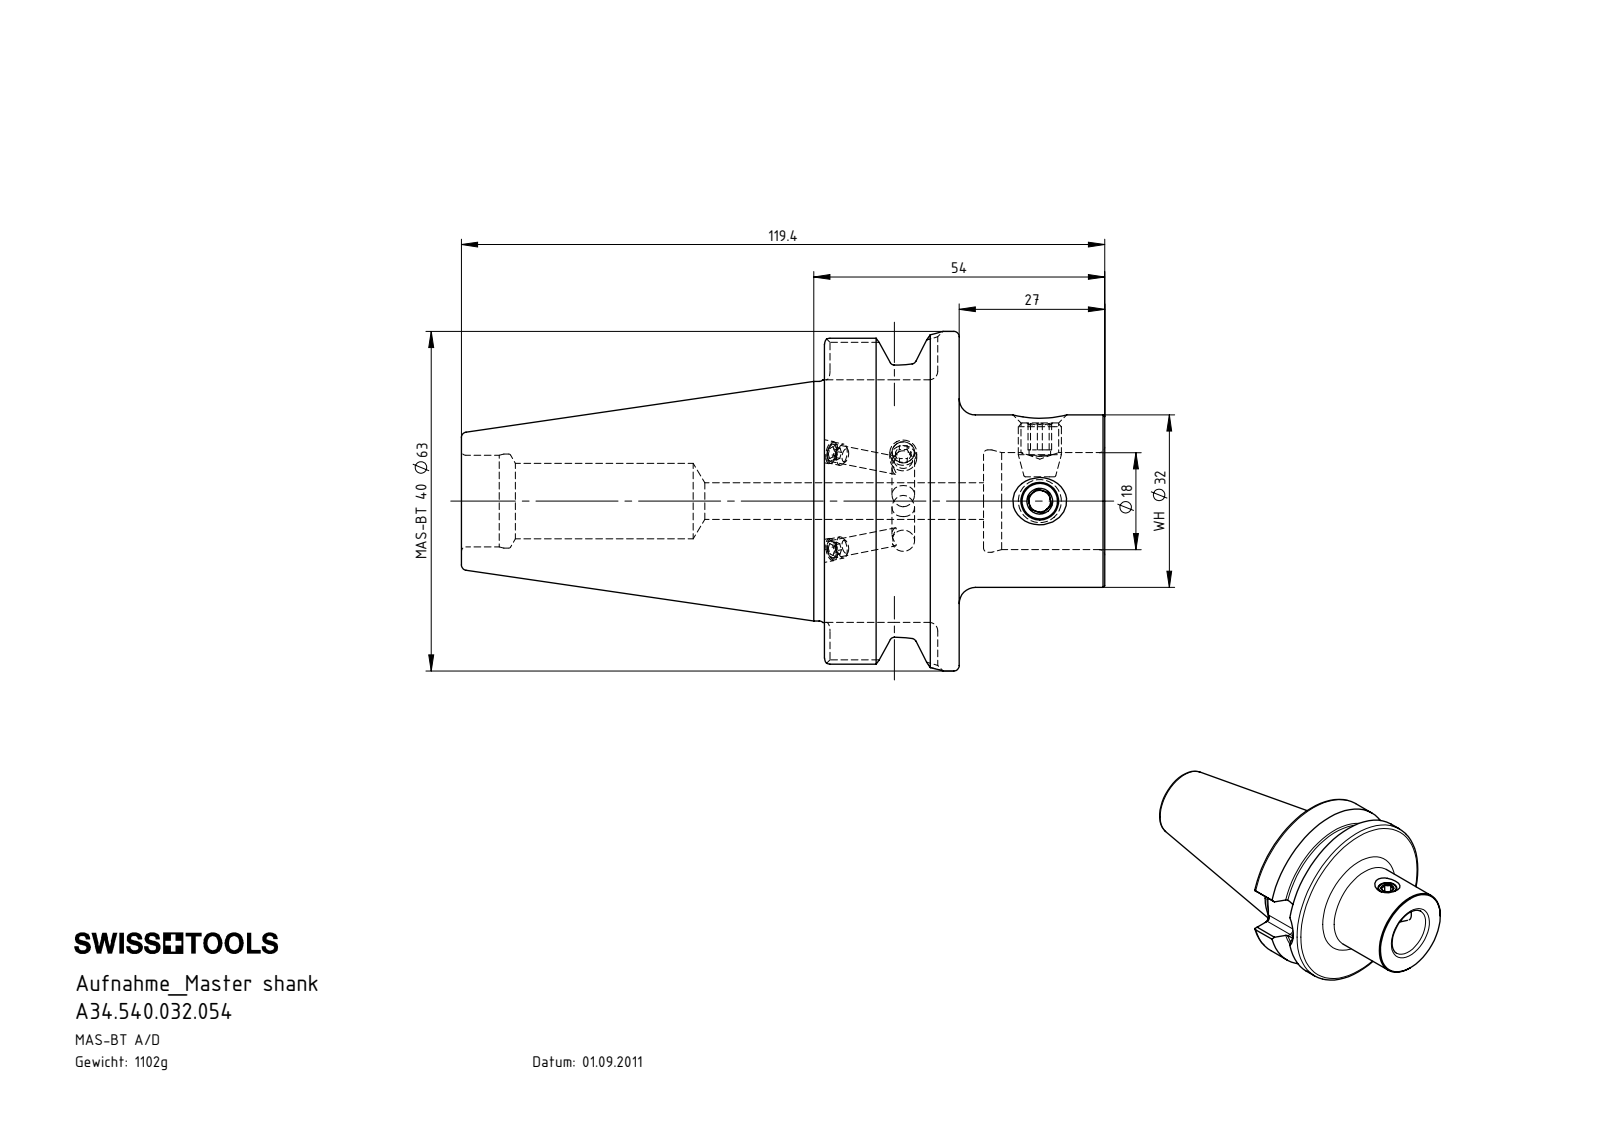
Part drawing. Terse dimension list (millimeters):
name: BB4-WH3.K01.054; BB4-WH3.K01.054_B; ISO 4026 - M5 x 4_PreviewCfg; ISO 4026 - M4 x 3_PreviewCfg (+1 more)
written by: SolidWorks 2015 (AUTOMOTIVE_DESIGN)
unit: mm
bodies: 6 solids, 228 faces (75 planar, 64 cylindrical, 89 other)
size: 119.4 × 63 × 63
volume: 140 407 mm³; area: 27 104 mm²
holes: 3× ⌀4.2, 2× ⌀3.3, 2× ⌀4, 2× ⌀7, 1× ⌀6.8, 1× ⌀14, 1× ⌀17, 1× ⌀17.45, 1× ⌀18, 1× ⌀19
bosses: 2× ⌀8, 2× ⌀4, 1× ⌀63, 1× ⌀53, 1× ⌀44.45, 1× ⌀32, 1× ⌀5
rounds: 8× R1.6, 1× R8.05
face distances: 25, 52, 27, 45, 29.5, 4.5, 22.5, 67.4, 92.4, 96.9
